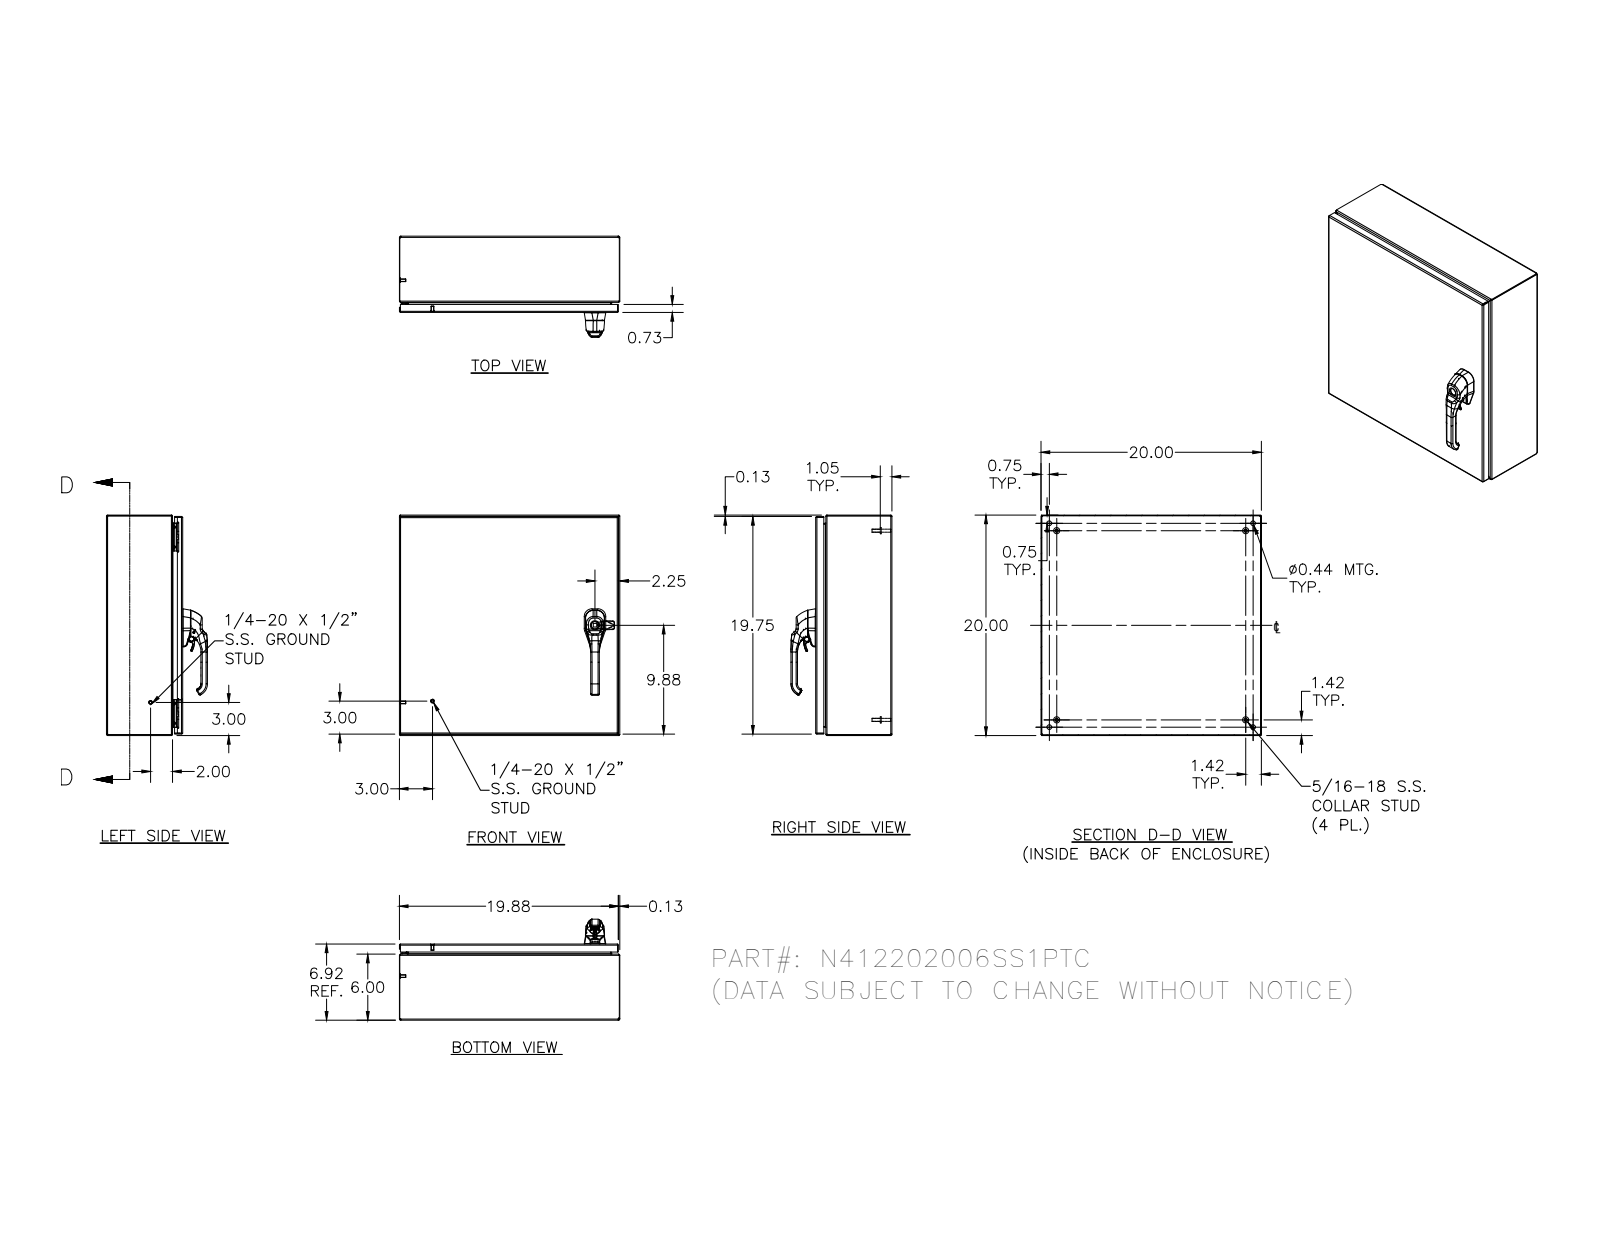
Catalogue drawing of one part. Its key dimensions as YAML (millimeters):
part_name: "N412202006SS1PTC; N412202006SS1PTCBKP; N4122020SS1PTCLID; HFW328176 (+8 more)"
step_written_by: "Autodesk Inventor 2012 (AUTOMOTIVE_DESIGN)"
units: millimeters
bodies: {solids: 41, faces: 2782, planar: 882, cylindrical: 1035, other: 865}
overall_size: [508, 508, 232.8]
volume: 1865000
surface_area: 1932000
round_holes:
  - {diameter: 2.4, count: 4}
  - {diameter: 3.9, count: 4}
  - {diameter: 4.2, count: 4}
  - {diameter: 4.4, count: 4}
  - {diameter: 4.8, count: 4}
  - {diameter: 11.1, count: 4}
  - {diameter: 5.4, count: 3}
  - {diameter: 7.1, count: 3}
  - {diameter: 4, count: 2}
  - {diameter: 8, count: 2}
  - {diameter: 10.2, count: 2}
  - {diameter: 10.5, count: 2}
round_bosses_or_shafts:
  - {diameter: 6.4, count: 10}
  - {diameter: 14.3, count: 4}
  - {diameter: 9.1, count: 4}
  - {diameter: 8.1, count: 4}
  - {diameter: 7.6, count: 4}
  - {diameter: 7, count: 4}
  - {diameter: 6.5, count: 4}
  - {diameter: 4.2, count: 4}
partial_cylinders:
  - {radius: 0.5, count: 174}
  - {radius: 0.3, count: 101}
  - {radius: 0.8, count: 30}
  - {radius: 1.3, count: 26}
  - {radius: 0.5, count: 21}
  - {radius: 2.7, count: 20}
  - {radius: 0.4, count: 18}
  - {radius: 2, count: 14}
face_to_face_distances: [1.9, 173.8, 506.1, 175.7, 171.9, 504.2, 508, 150.5, 23.3, 18.8]
hole_center_spacings: [406.3, 469.9, 479.3, 0.4, 16.8, 406.5, 423.1, 0.5]
